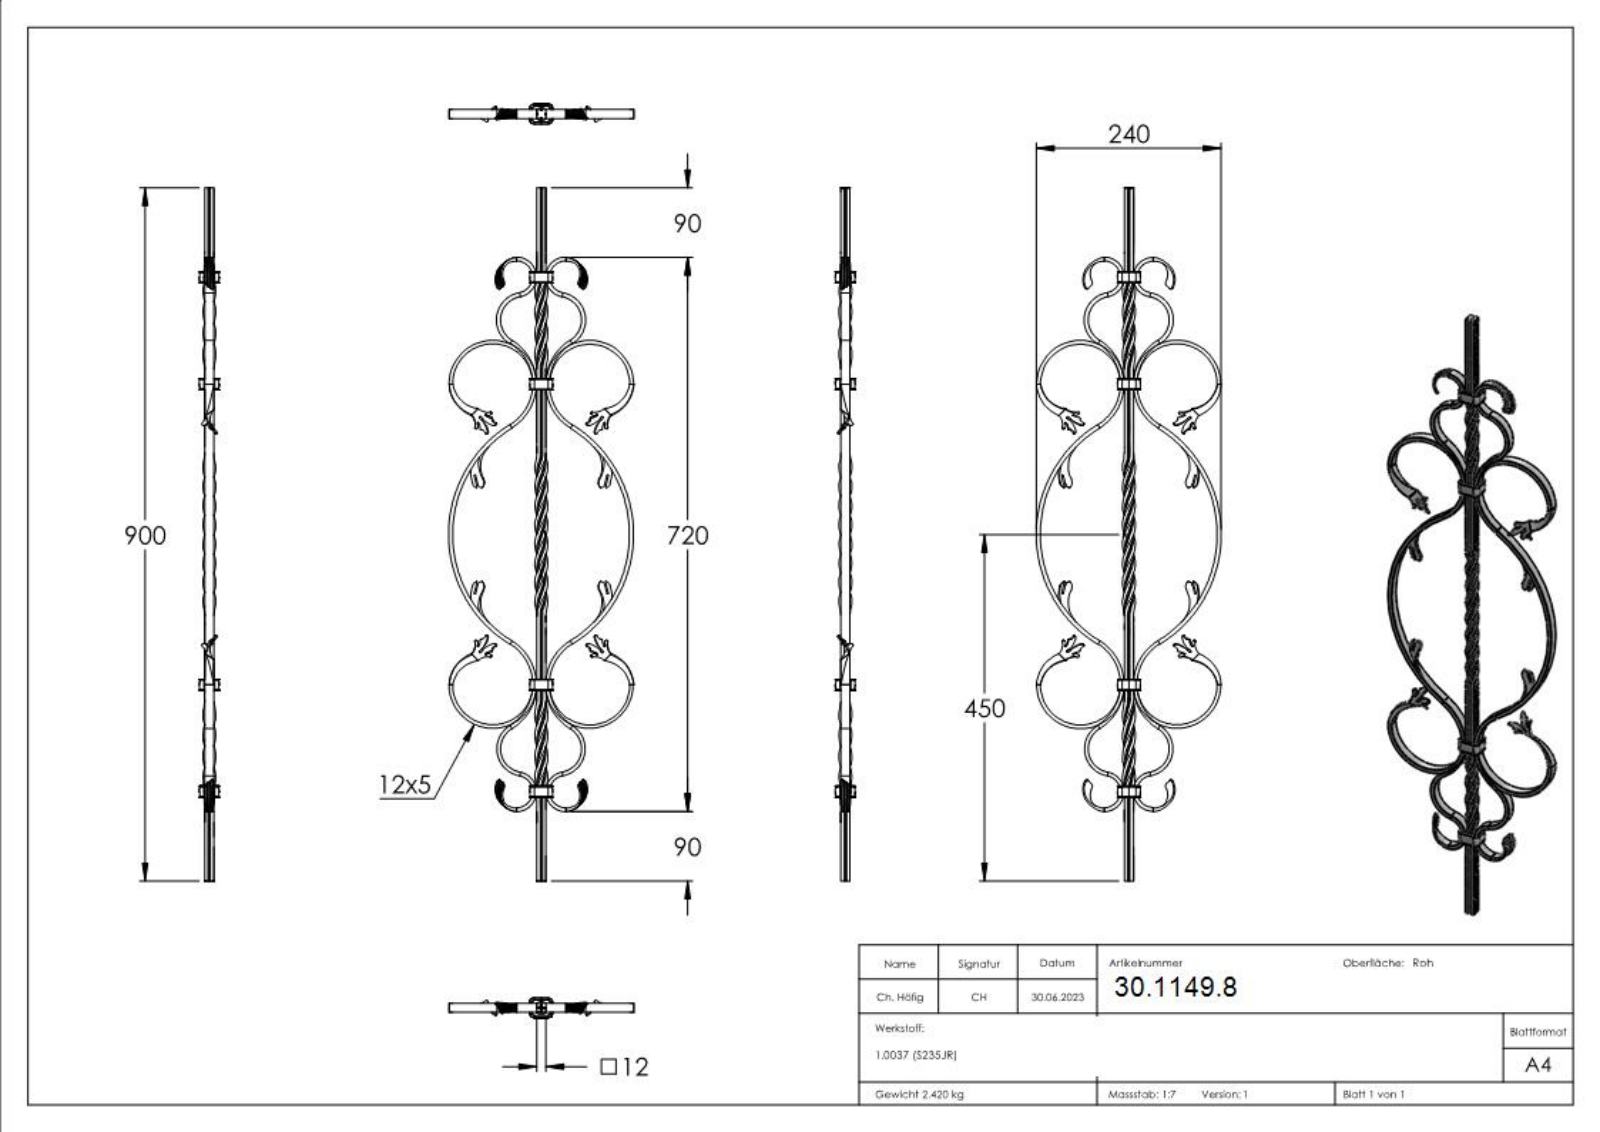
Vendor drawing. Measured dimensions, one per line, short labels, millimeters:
name: 1502
written by: SolidWorks 2018 (CONFIG_CONTROL_DESIGN)
unit: mm
bodies: 19 solids, 1047 faces (349 planar, 60 cylindrical, 638 other)
size: 900 × 240 × 25.85
volume: 310 490 mm³; area: 169 744 mm²
rounds: 12× R1, 8× R1.07, 4× R20.75, 4× R25.75, 4× R30.77, 4× R35.77, 4× R52, 4× R57
face distances: 12, 3.93, 15.93, 529.5, 139, 24, 15, 19.85, 15.92, 3.92
